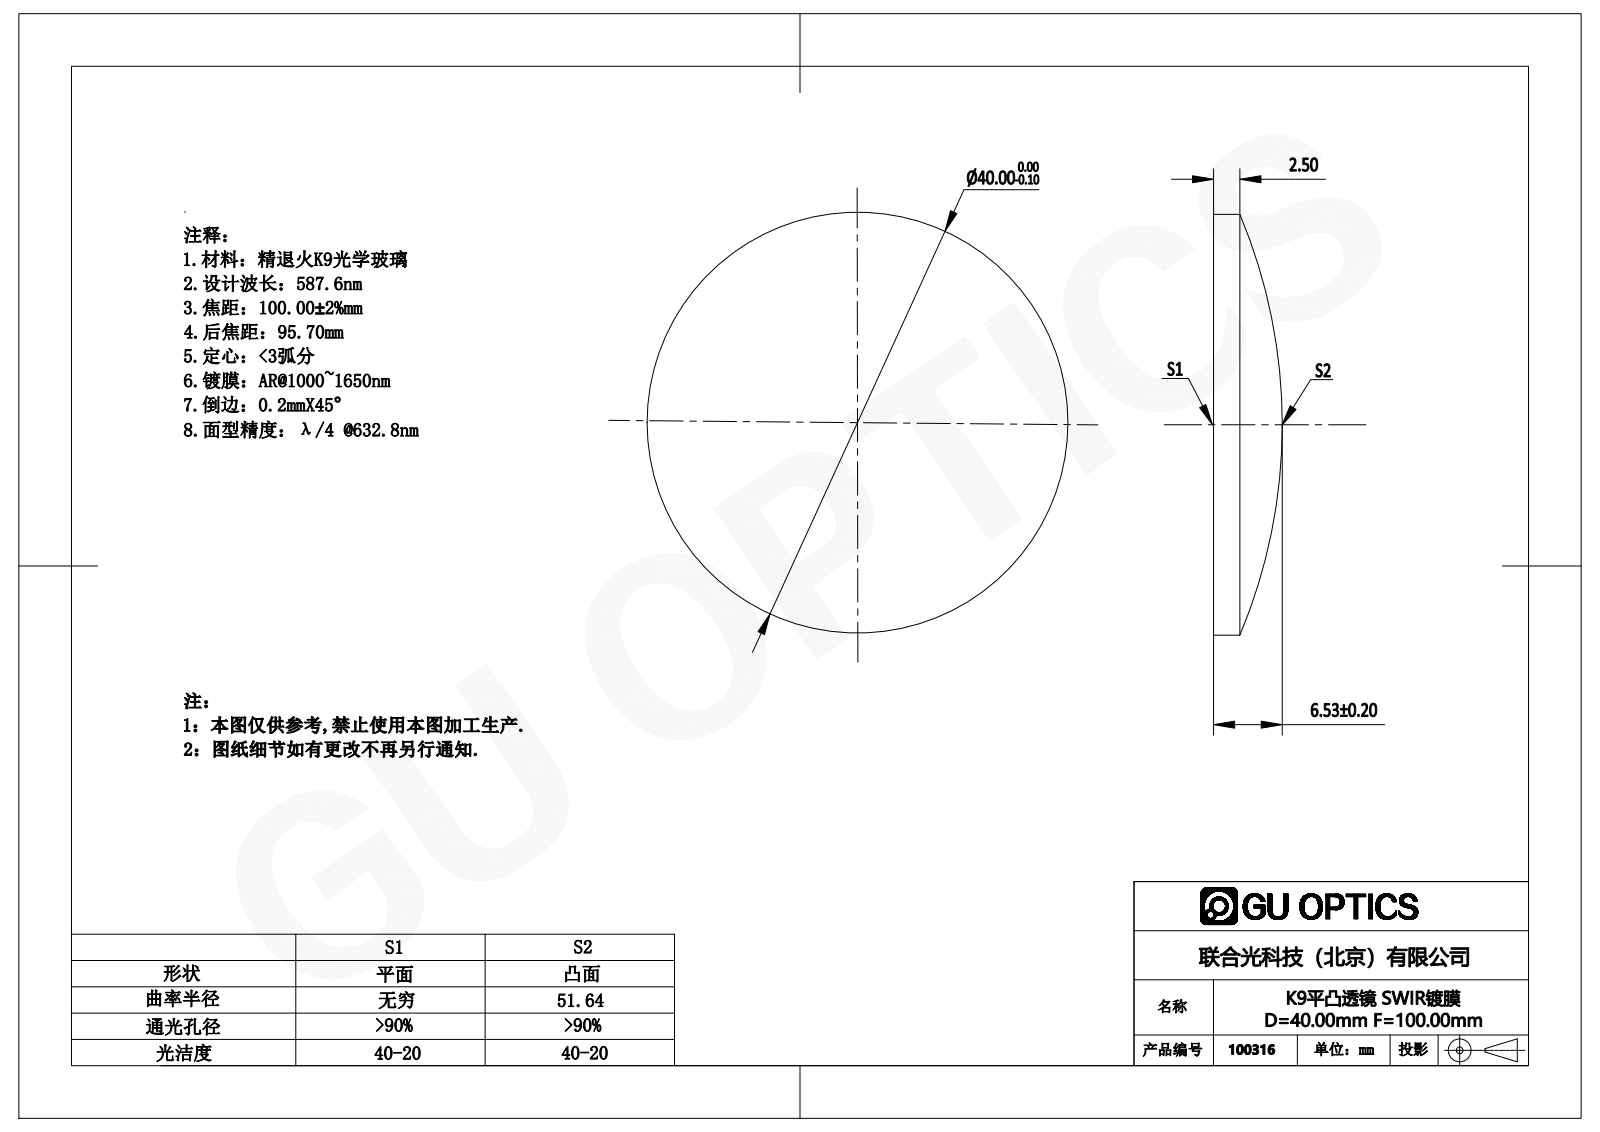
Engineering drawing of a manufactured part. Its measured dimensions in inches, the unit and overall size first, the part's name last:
Units: inches
Overall size (bounding box): 1.575 × 1.575 × 0.257
Round bosses / shafts (diameter × count): ⌀1.575 ×1
Volume: 0.348 in³ · Surface area: 4.461 in²
Bodies: 1 solid, 5 faces (1 planar, 2 cylindrical, 2 other)
Part name (STEP PRODUCT): 100144
STEP written by: SolidWorks 2016 (AUTOMOTIVE_DESIGN)
